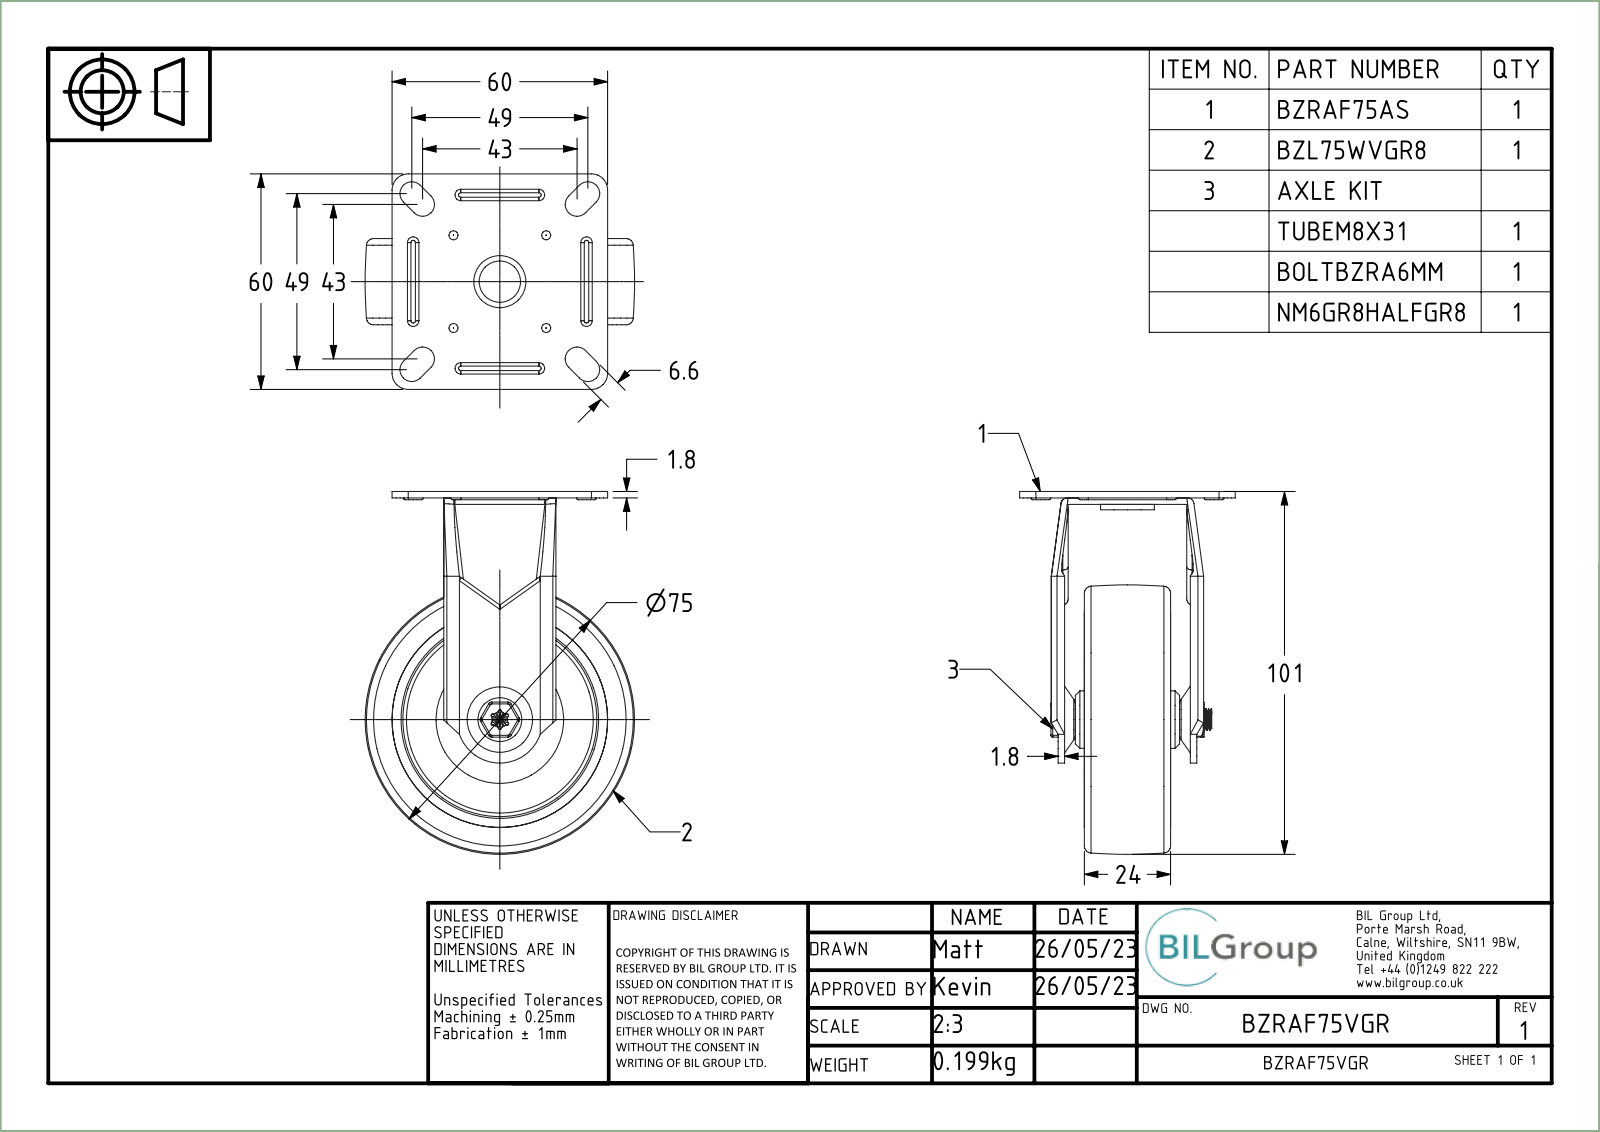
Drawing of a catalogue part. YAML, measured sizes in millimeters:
part_name: "BZRAF75AS; ZINC PLATED PRESSED STEEL TOP PLATE; ZINC PLATED PRESSED STEEL FORKS; BZRAF75VGR (+8 more)"
step_written_by: "Spatial InterOp 3D (CONFIG_CONTROL_DESIGN)"
units: millimeters
bodies: {solids: 7, faces: 491, planar: 107, cylindrical: 214, other: 170}
overall_size: [101, 75, 60]
volume: 81279
surface_area: 50136
round_holes:
  - {diameter: 6, count: 1}
  - {diameter: 6.2, count: 1}
  - {diameter: 6.4, count: 1}
  - {diameter: 8.2, count: 1}
  - {diameter: 8.4, count: 1}
  - {diameter: 11.5, count: 1}
  - {diameter: 12, count: 1}
  - {diameter: 54, count: 1}
  - {diameter: 60, count: 1}
round_bosses_or_shafts:
  - {diameter: 16, count: 1}
  - {diameter: 15, count: 1}
  - {diameter: 8, count: 1}
  - {diameter: 5, count: 1}
partial_cylinders:
  - {radius: 1, count: 34}
  - {radius: 0.5, count: 20}
  - {radius: 1.5, count: 8}
  - {radius: 3.3, count: 8}
  - {radius: 0.4, count: 6}
  - {radius: 0.99, count: 4}
  - {radius: 4.5, count: 4}
  - {radius: 1.8, count: 2}
face_to_face_distances: [1.8, 10, 14, 35.8, 1, 15.5, 5.5, 19.5, 29.5, 24]
